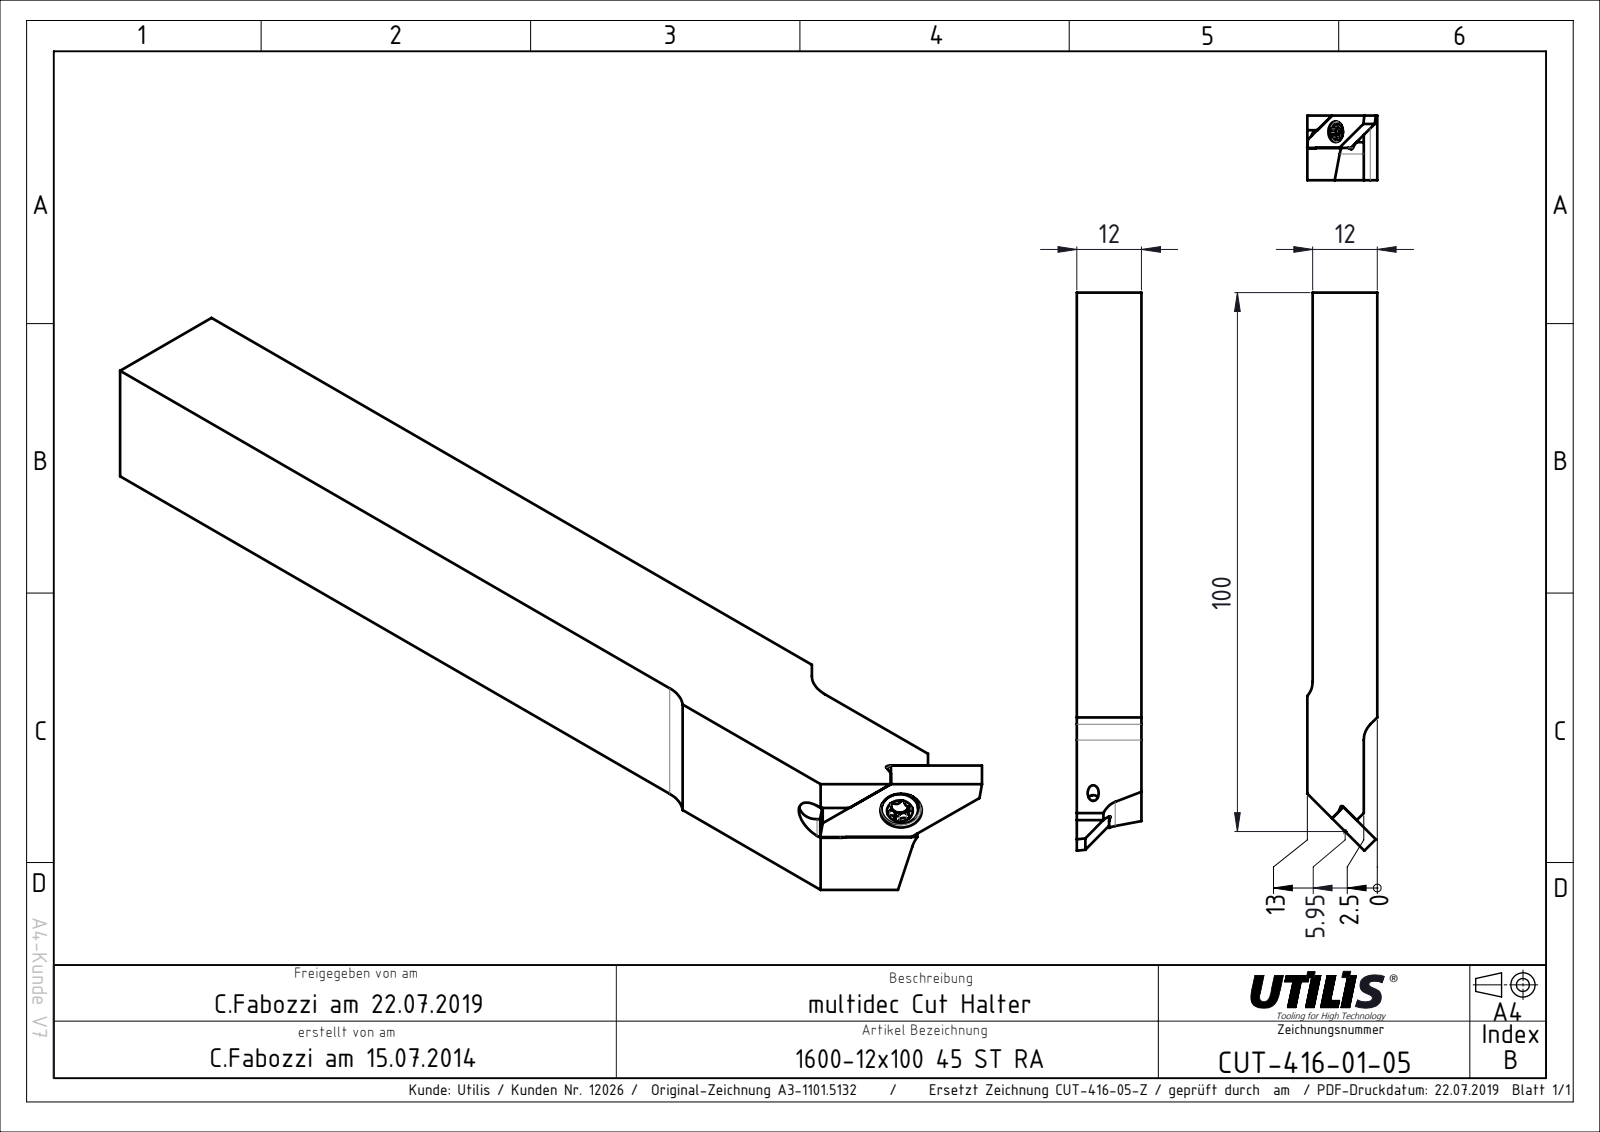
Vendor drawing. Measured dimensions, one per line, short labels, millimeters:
name: CUT-416_05; CUT-Vorlage 1600_1600 Vorlage; CUT-416-01-05
written by: SolidWorks 2020 (AUTOMOTIVE_DESIGN)
unit: mm
bodies: 2 solids, 41 faces (26 planar, 8 cylindrical, 7 other)
size: 103.54 × 13.02 × 12
volume: 13 674 mm³; area: 5 135 mm²
holes: 1× ⌀2.9, 1× ⌀3.1
rounds: 3× R4.1, 1× R0.5, 1× R1.55, 1× R1.7
face distances: 12, 13, 1, 2.5, 9.5, 10.5, 6, 3, 6.01, 10.78
